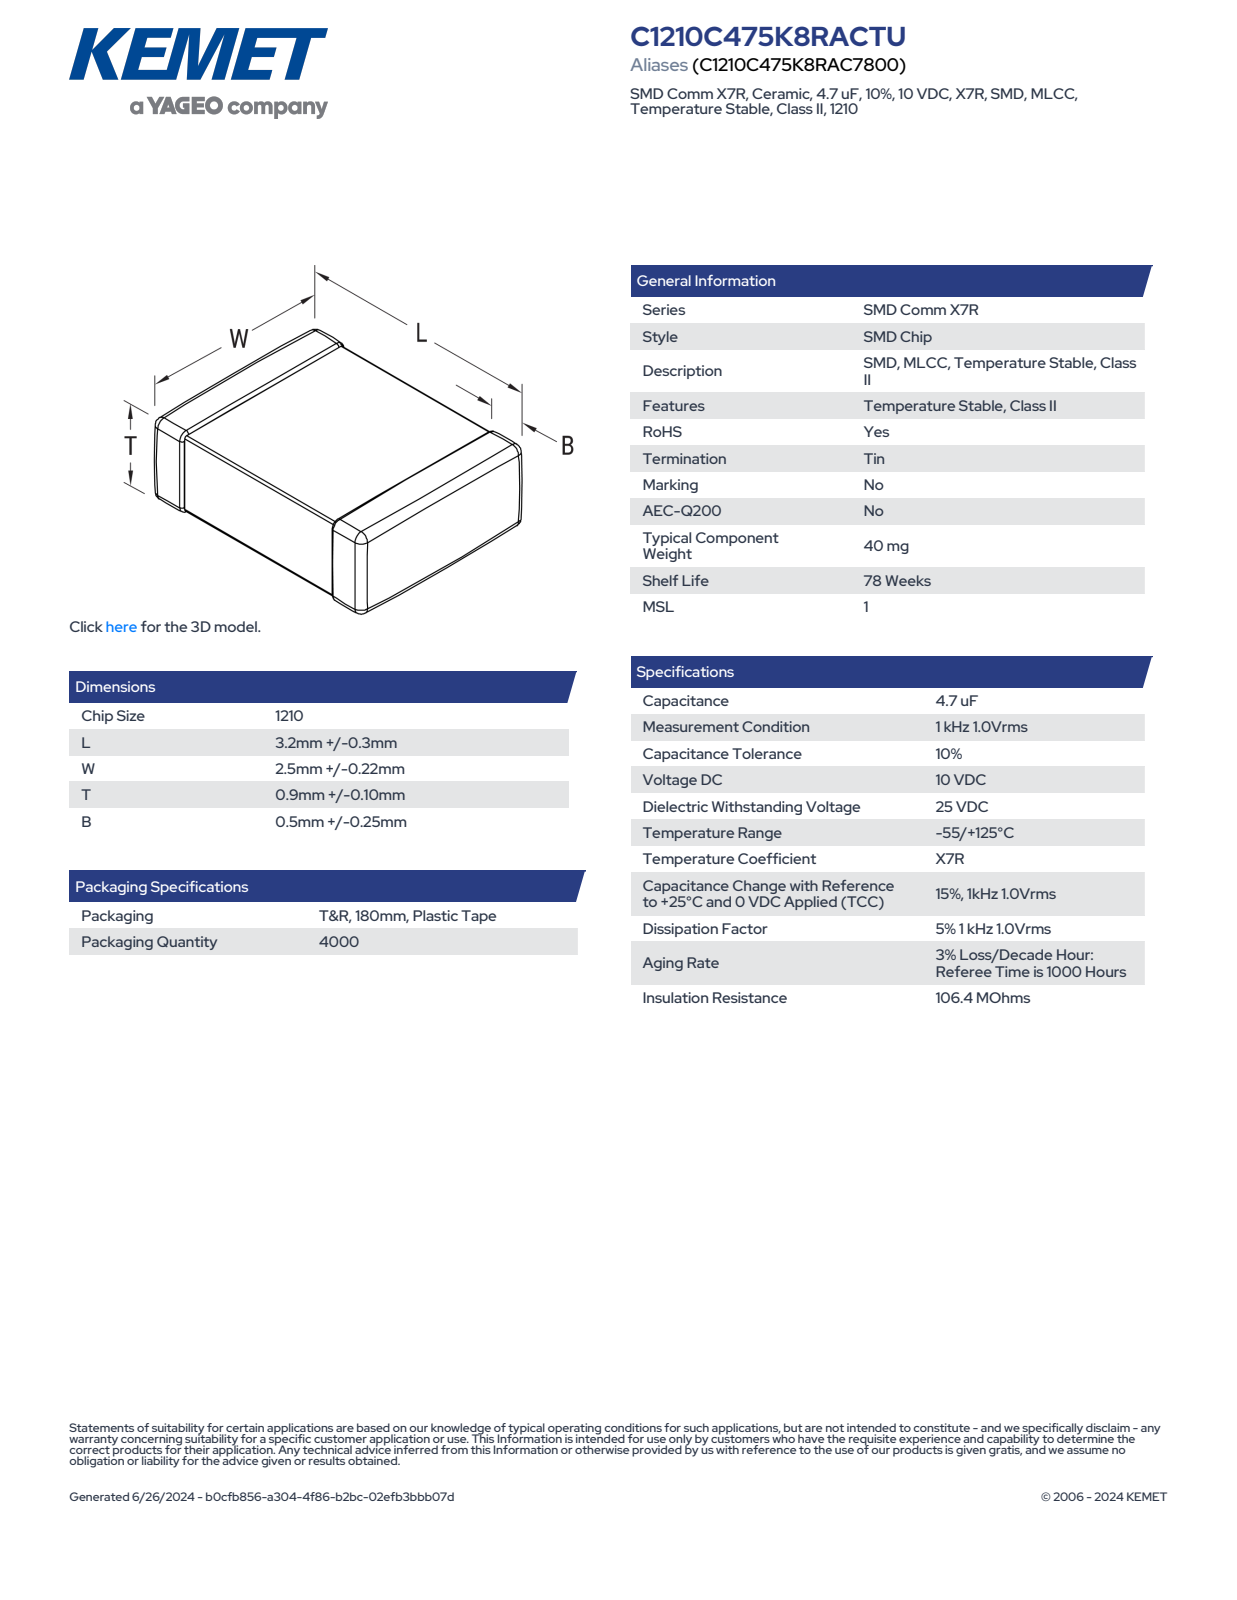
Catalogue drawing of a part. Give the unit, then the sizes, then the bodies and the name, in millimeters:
Units: millimetres
Overall size (bounding box): 3.5 × 2.72 × 1
Main face-to-face distances: 0.94, 0.88, 1, 3.5, 2.66, 2.6, 2.72, 0.95, 0.89, 1.49
Volume: 9 mm³ · Surface area: 31 mm²
Bodies: 4 solids, 125 faces (71 planar, 38 cylindrical, 16 other)
Part name (STEP PRODUCT): CCS_CCSTD_1210_L3.5W2.72T1B0.5
STEP written by: SolidWorks 2021 (AUTOMOTIVE_DESIGN)
